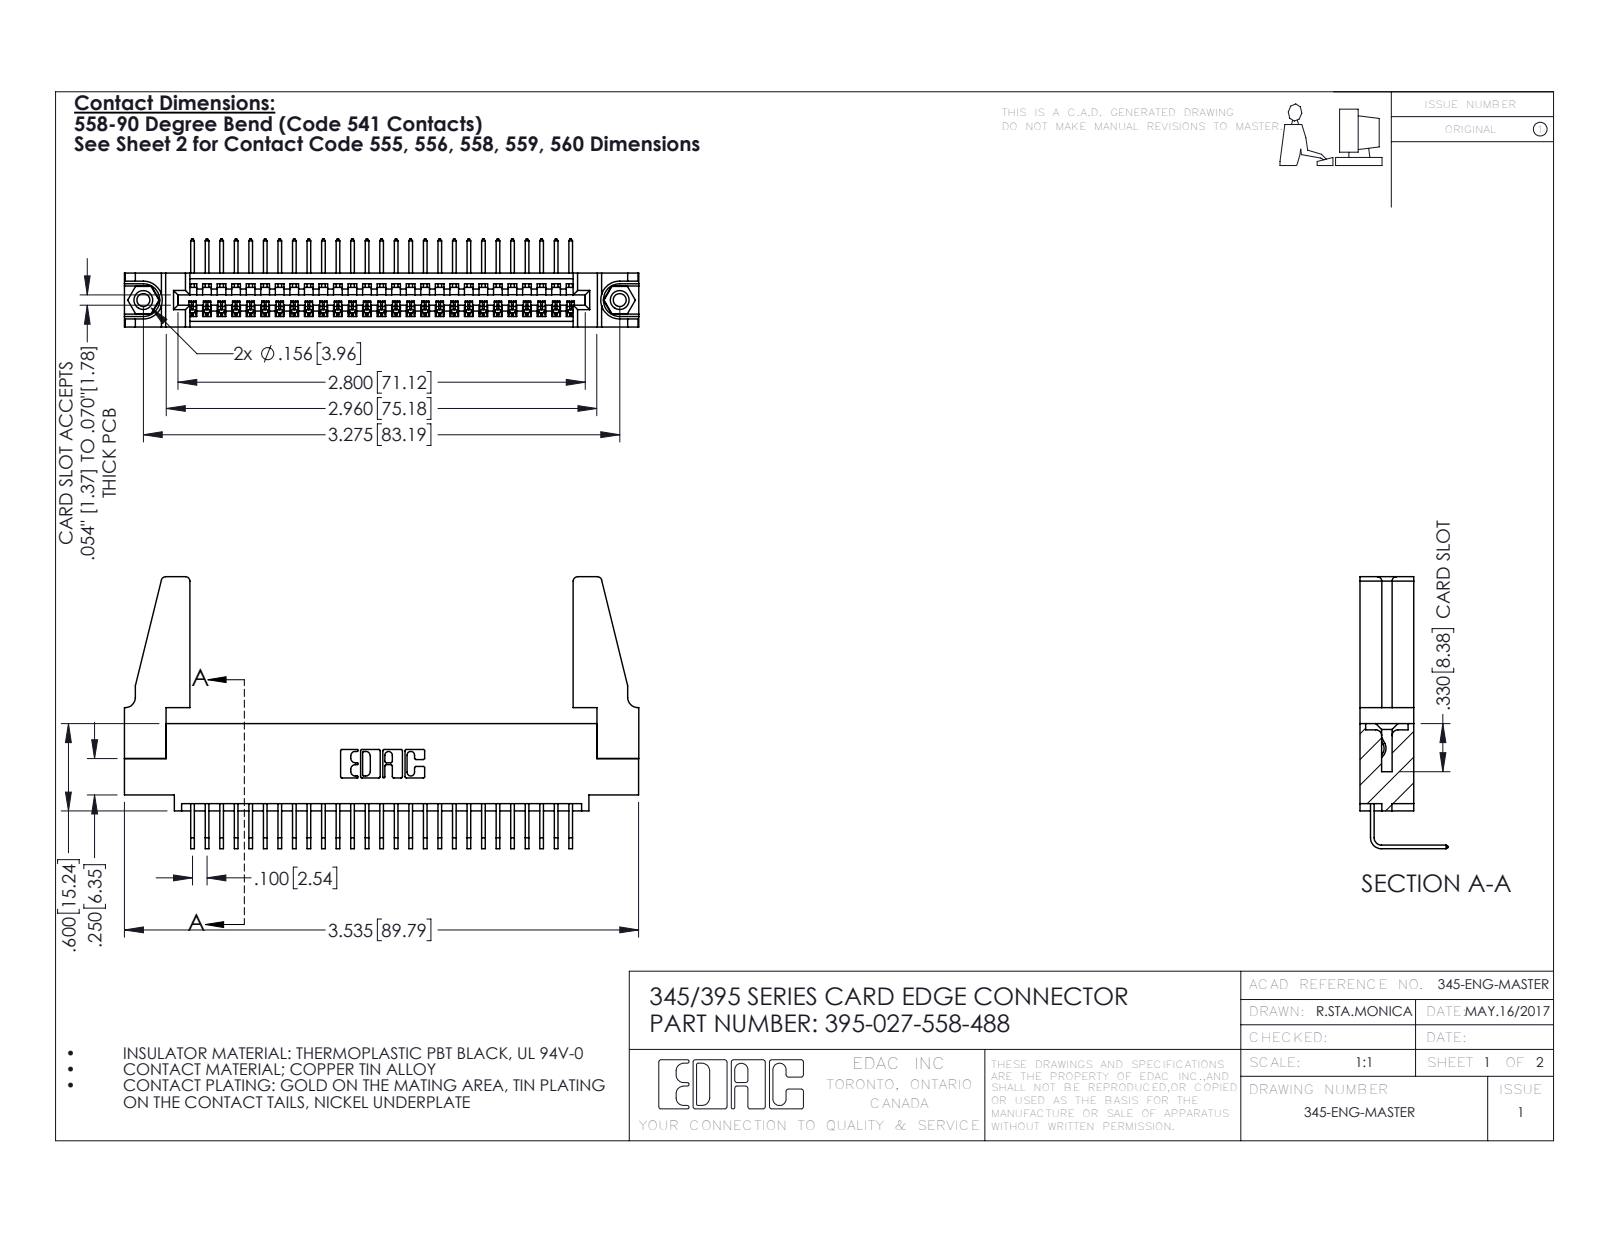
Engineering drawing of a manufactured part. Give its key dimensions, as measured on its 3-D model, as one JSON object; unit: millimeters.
{"part_name": "345-220-078_345-220-088; 395-027-558-488; 345 Part_0.110 Offset - 0.156 Dia-TH; 345-250-001_345-250-001-102 (+1 more)", "step_written_by": "SolidWorks 2016 (CONFIG_CONTROL_DESIGN)", "units": "millimeters", "bodies": {"solids": 32, "faces": 1874, "planar": 1290, "cylindrical": 568, "other": 16}, "overall_size": [89.8, 47.5, 15.4], "volume_mm3": 11700, "surface_area_mm2": 14730, "round_holes": [[2.3, 2], [3.2, 2], [4, 2], [1.6, 1]], "round_bosses_or_shafts": [[3.9, 2]], "partial_cylinders_radius": [[0.2, 54], [0.3, 22], [0.8, 8], [0.2, 6], [0.8, 6], [0.7, 3], [0.8, 2], [1, 2]], "face_to_face_distances": [1.8, 9.4, 7.6, 5.1, 2.5, 6.9, 0.6, 5.7, 3.8, 1.8], "hole_center_spacings": [6.9, 77.2, 83.2]}
